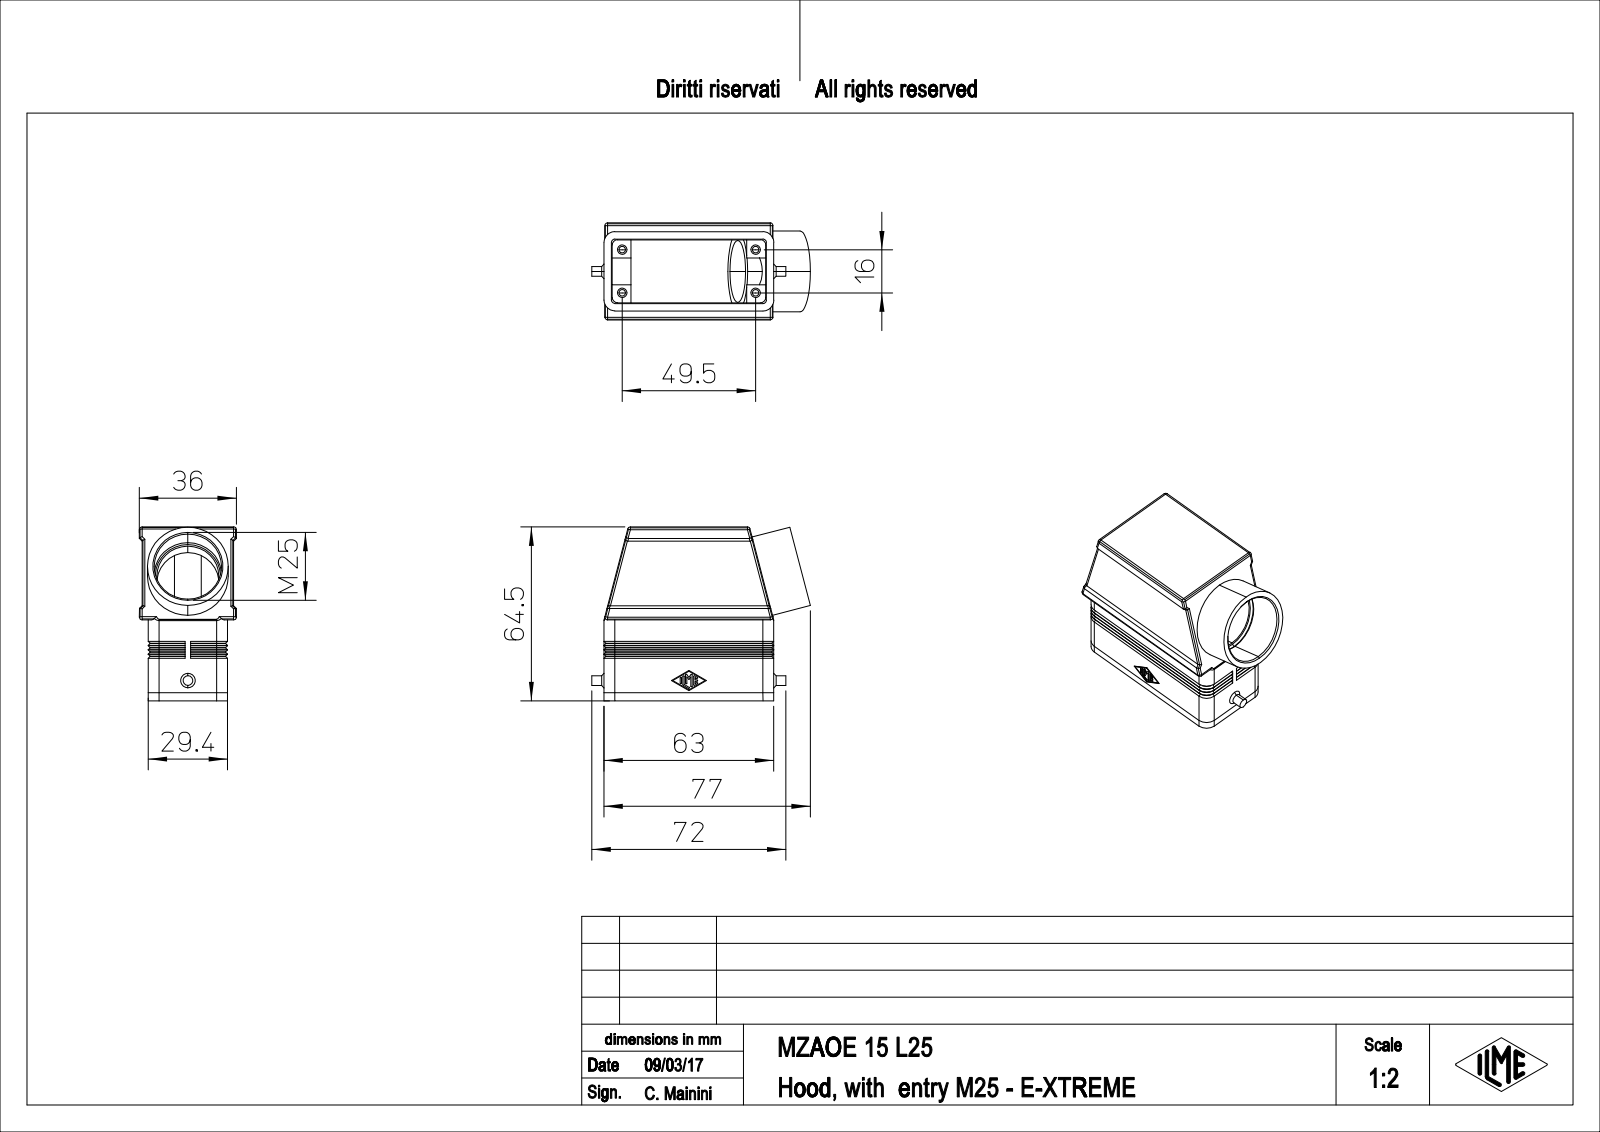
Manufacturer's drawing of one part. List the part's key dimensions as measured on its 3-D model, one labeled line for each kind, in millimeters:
Part name (STEP PRODUCT): MZAOE_15_L25
STEP written by: PTC Creo Elements/Direct Modeling 19.0E 27-Jun-2016 (C) Parametric Technology GmbH (AUTOMOTIVE_DESIGN)
Units: millimetres
Bodies: 1 solid, 412 faces (194 planar, 156 cylindrical, 62 other)
Overall size (bounding box): 81.08 × 64.5 × 36
Volume: 49 545 mm³ · Surface area: 29 105 mm²
Round holes (diameter × count): ⌀2.46 ×4, ⌀3.5 ×4, ⌀23 ×1, ⌀25 ×1, ⌀30 ×1
Round bosses / shafts (diameter × count): ⌀30 ×1, ⌀29 ×1, ⌀3.6 ×1
Partial cylindrical surfaces — rounded edges, fillets, slot ends (radius × count): R1 ×24, R0.25 ×14, R4 ×8, R2 ×6, R1.25 ×4, R3.3 ×4
Main face-to-face distances: 3, 28.7, 5.3, 23.4, 2.3, 31.7, 26.4, 34, 29.4, 10
Hole centre spacings: 16, 49.5, 52.02
